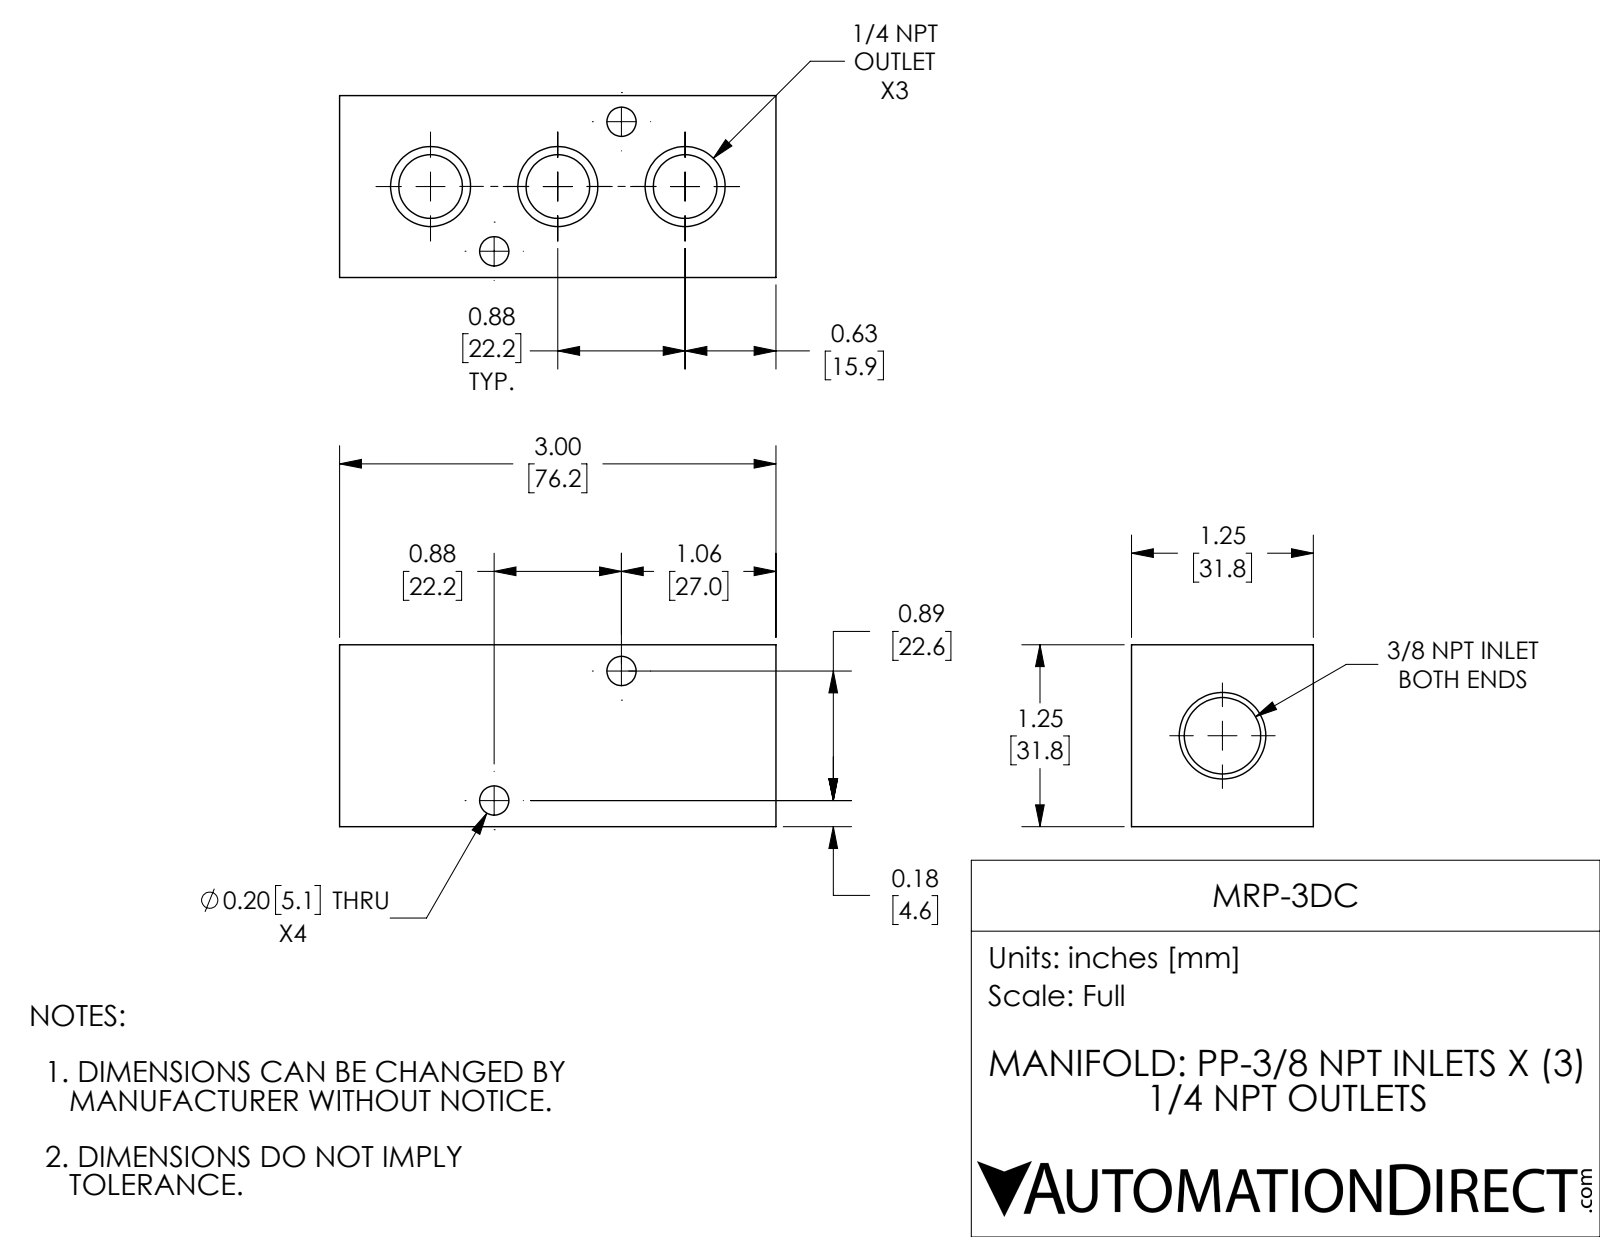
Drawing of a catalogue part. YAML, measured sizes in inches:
part_name: "MRP-3DC"
step_written_by: "SolidWorks 2018 (AUTOMOTIVE_DESIGN)"
units: inches
bodies: {solids: 1, faces: 40, planar: 6, cylindrical: 24, other: 10}
overall_size: [3, 1.25, 1.25]
volume: 3.706
surface_area: 25.79
round_holes:
  - {diameter: 0.201, count: 4}
  - {diameter: 0.438, count: 3}
  - {diameter: 0.525, count: 1}
face_to_face_distances: [1.25, 3]
hole_center_spacings: [0.624, 0.875, 1.248, 1.385, 1.75]
